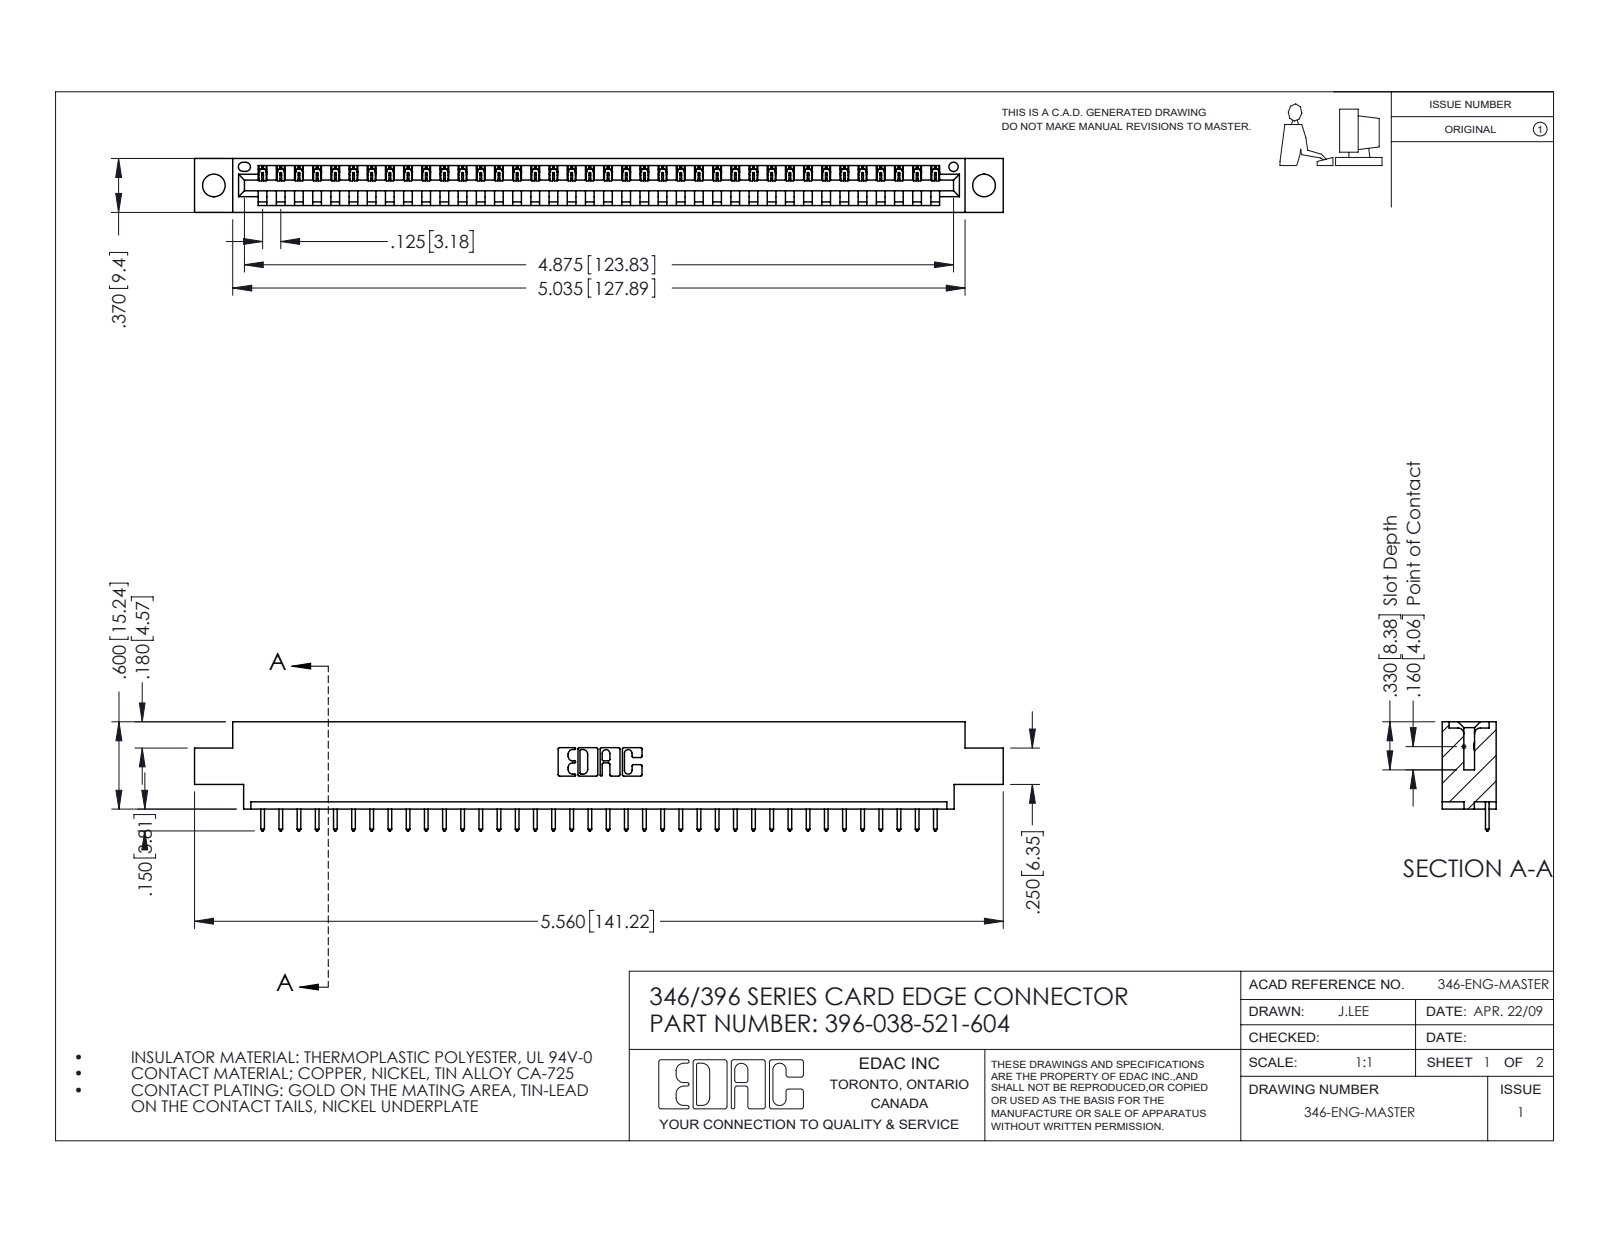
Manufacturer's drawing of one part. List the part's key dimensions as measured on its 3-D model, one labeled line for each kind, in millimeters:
Part name (STEP PRODUCT): 346 Part_0.170 Offset - 0.156 Dia-TH; 396-038-521-604; 345-292-001_345-293-121
STEP written by: SolidWorks 2016 (CONFIG_CONTROL_DESIGN)
Units: millimetres
Bodies: 39 solids, 2330 faces (1600 planar, 730 cylindrical, 0 other)
Overall size (bounding box): 141.2 × 19.1 × 9.4
Volume: 13 100 mm³ · Surface area: 15 920 mm²
Round holes (diameter × count): ⌀4 ×2, ⌀1.6 ×1
Partial cylindrical surfaces — rounded edges, fillets, slot ends (radius × count): R0.2 ×76, R0.3 ×76, R0.3 ×22, R0.2 ×6, R0.8 ×6, R0.7 ×3, R0.8 ×2, R1 ×2
Main face-to-face distances: 1.2, 8.2, 9.4, 6.4, 1.8, 7.6, 0.6, 3.8, 5.6, 2.5
Hole centre spacings: 6.2, 129.2, 134.5
